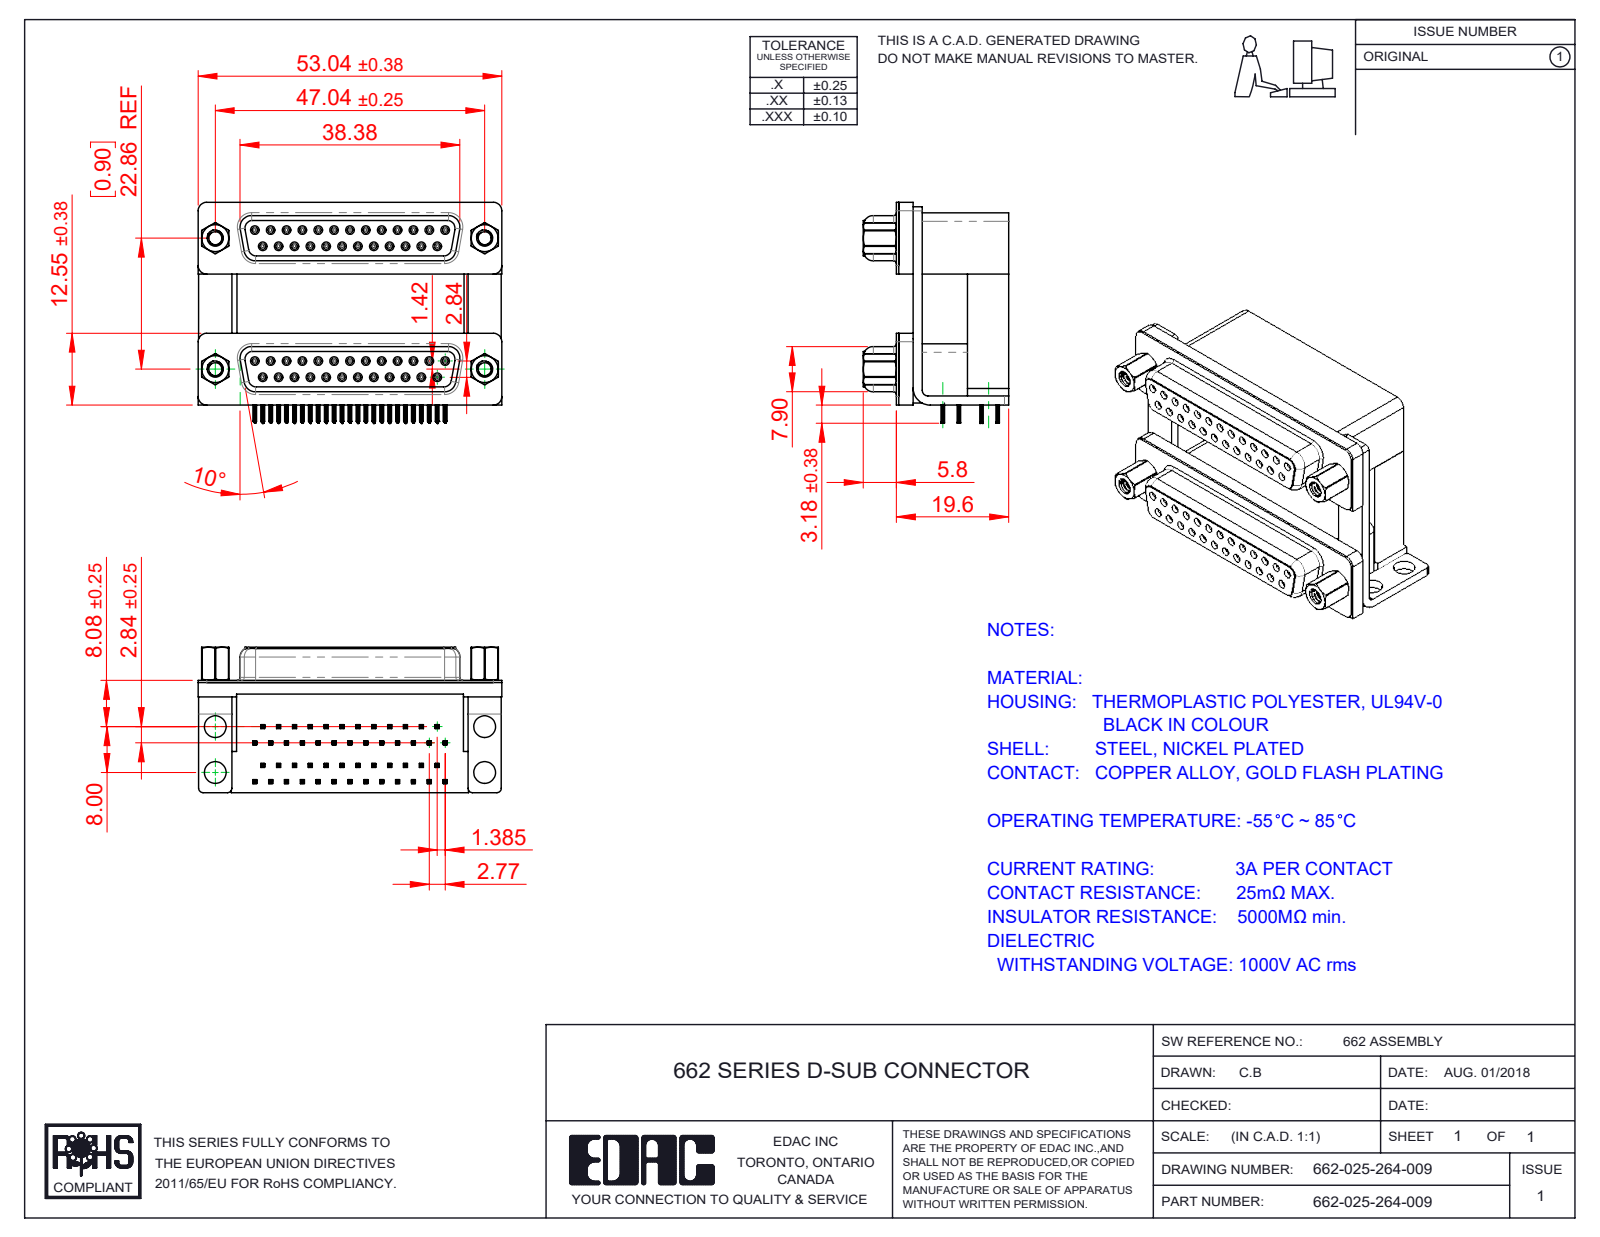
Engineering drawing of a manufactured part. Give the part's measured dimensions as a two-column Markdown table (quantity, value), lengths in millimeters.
| quantity | value |
| --- | --- |
| part name | 662 Mounting Bracket_NoneH; 662 Contact Bottom Upper_H; 662 4-40 Hex Standoff 5; 662 Shell_25 Contacts (+8 more) |
| STEP written by | SolidWorks 2020 (CONFIG_CONTROL_DESIGN) |
| units | millimeters |
| bodies | 65 solids, 8044 faces (3620 planar, 1948 cylindrical, 2476 other) |
| overall size | 53.04 × 38.59 × 25.4 |
| volume | 25 391 mm³ |
| surface area | 27 814 mm² |
| round holes (diameter × count) | 0.8 × 50, 0.9 × 50, 2.26 × 4, 2.29 × 4, 3.5 × 4, 3.8 × 4, 4 × 4, 4.8 × 4, 5 × 4 |
| round bosses / shafts (diameter × count) | 1.2 × 50, 4.9 × 4, 4.75 × 4, 3.9 × 4, 2.79 × 4 |
| partial cylindrical surfaces (radius × count) | 0.1 × 400, 0.15 × 200, 0.35 × 100, 0.34 × 50, 0.28 × 24, 1.35 × 16, 1.5 × 14, 0.5 × 8 |
| main face-to-face distances | 22.86, 19.2, 0.4, 7.2, 12, 6.2, 10.7, 2.84, 9.5, 16.7 |
| hole center spacings | 3.16, 2.77, 5.54, 11.08, 8.31, 5.03, 13.85, 7.48 |
